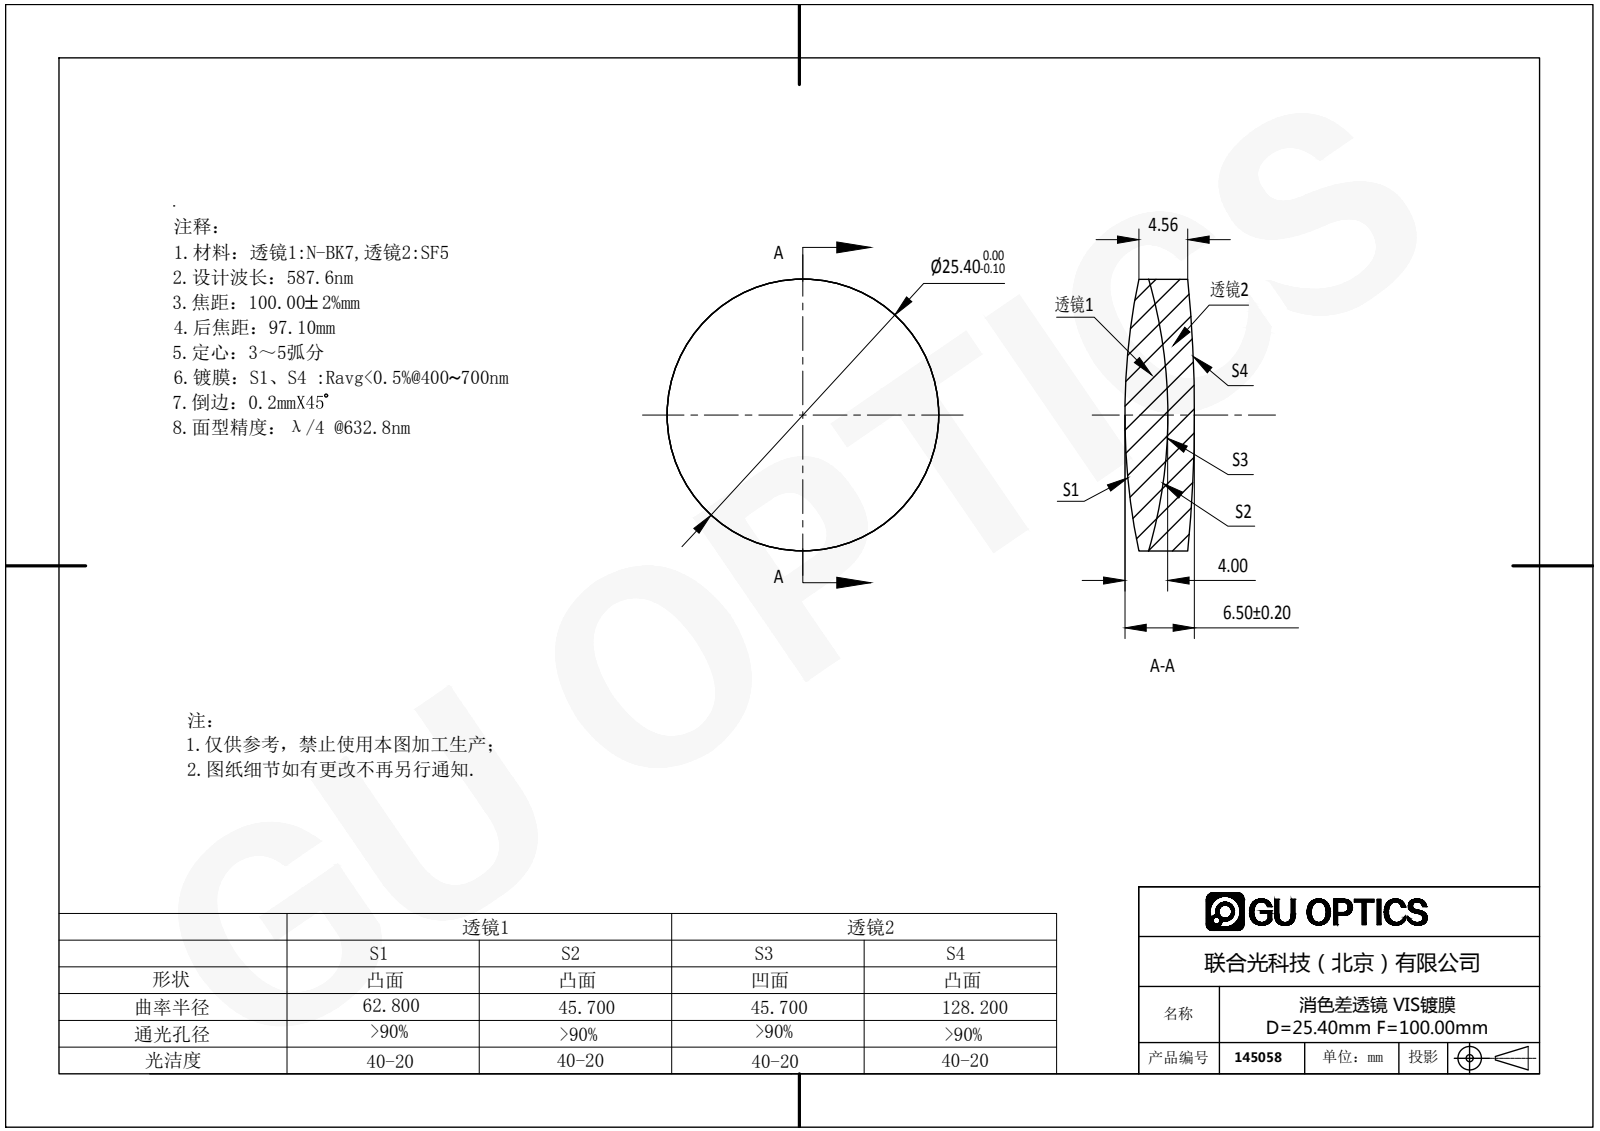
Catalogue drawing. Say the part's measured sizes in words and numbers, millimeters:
The part is named "145058". Its 3-D file was written by "SolidWorks 2016 (AUTOMOTIVE_DESIGN)". It is 2 solids with 12 faces: 0 planar, 4 cylindrical and 8 other. Overall it measures 25.4 by 25.4 by 6.5 millimeters. Its volume is 2 806 cubic millimeters and its surface area 2 419 square millimeters. Round bosses or shafts: 1 of diameter 25.4.
